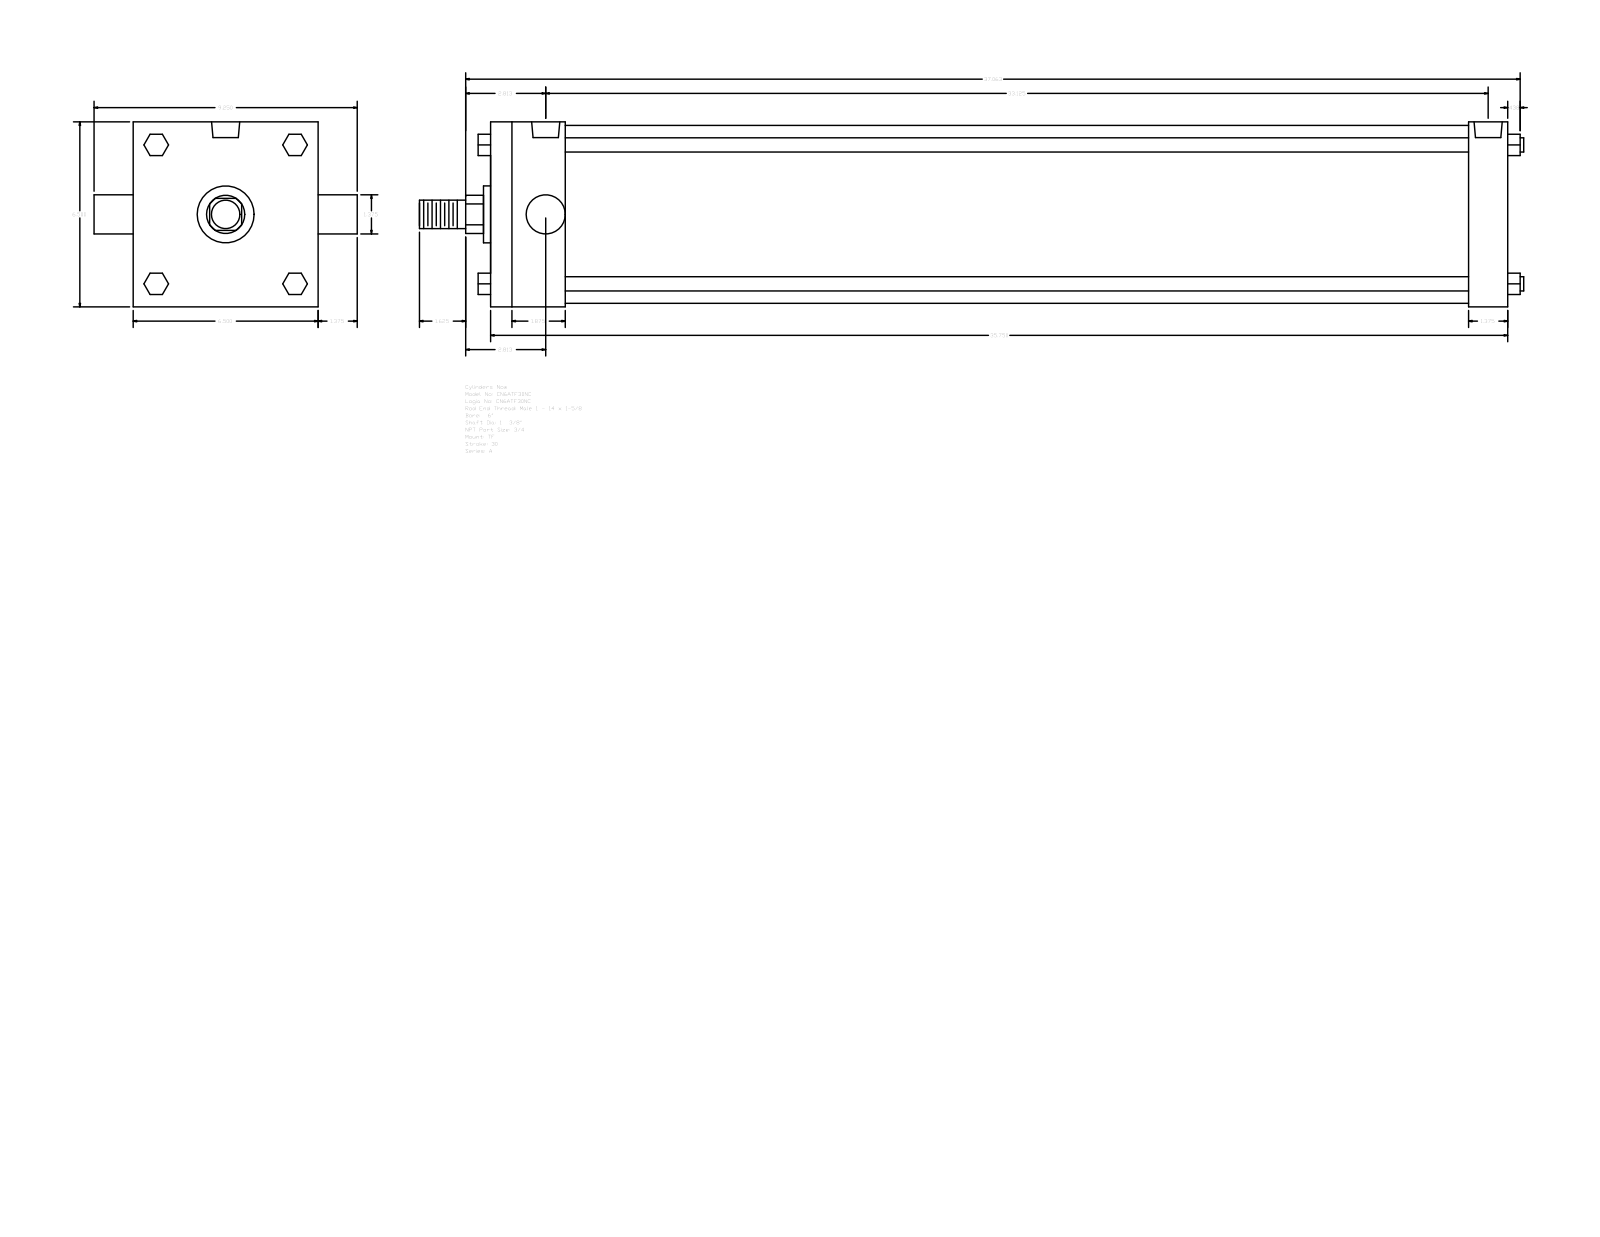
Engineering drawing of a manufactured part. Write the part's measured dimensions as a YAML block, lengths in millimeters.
part_name: "A_TF__0600_1.375"
step_written_by: "GSSL Pune (CONFIG_CONTROL_DESIGN)"
units: millimeters
bodies: {solids: 0, faces: 120, planar: 92, cylindrical: 28, other: 0}
overall_size: [985.84, 234.95, 165.1]
round_holes:
  - {diameter: 15.08, count: 3}
  - {diameter: 25.12, count: 2}
round_bosses_or_shafts:
  - {diameter: 12.7, count: 4}
  - {diameter: 34.92, count: 2}
  - {diameter: 158.75, count: 1}
  - {diameter: 50.8, count: 1}
  - {diameter: 25.4, count: 1}
partial_cylinders:
  - {radius: 17.06, count: 1}
face_to_face_distances: [165.1, 908.04, 34.92, 66.67, 841.37, 873.12, 806.45, 19.05, 61.97, 107.34]
hole_center_spacings: [5.56, 835.81, 830.25, 841.37]
